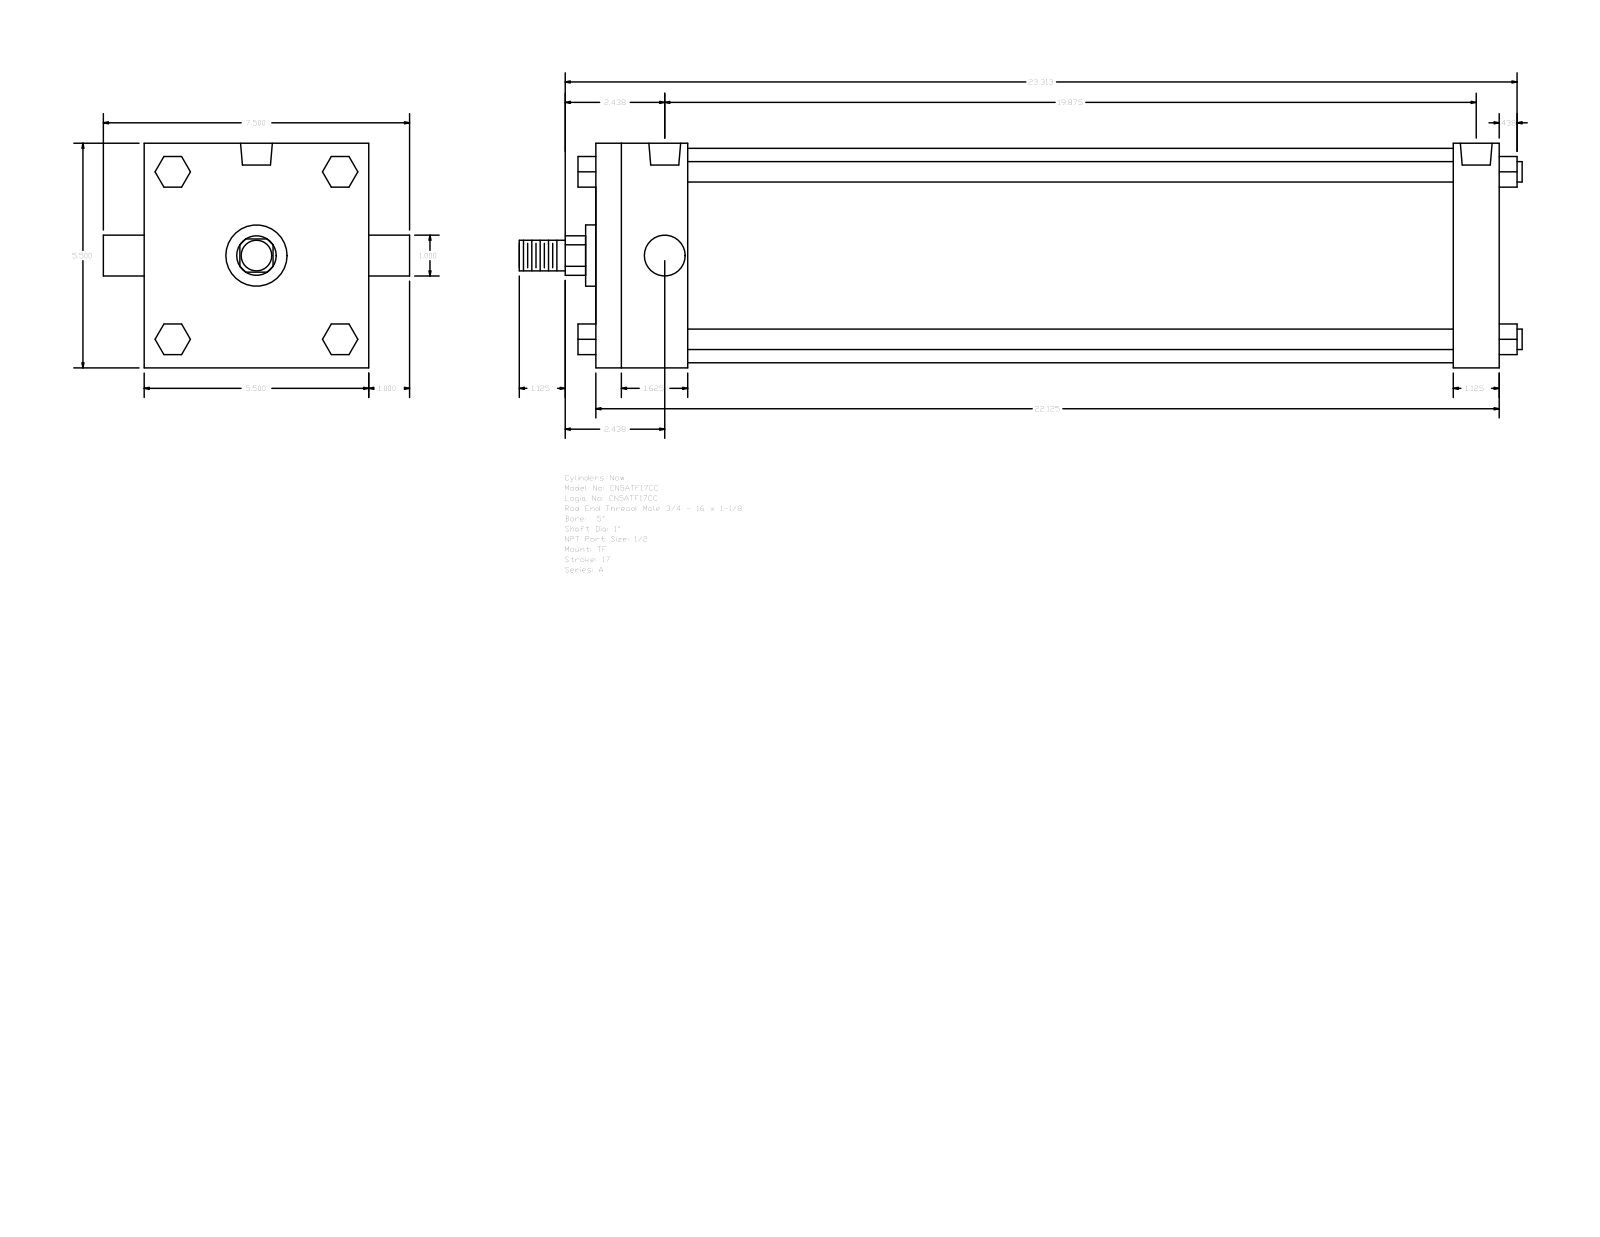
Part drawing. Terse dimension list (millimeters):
name: A_TF__0500_1
written by: GSSL Pune (CONFIG_CONTROL_DESIGN)
unit: mm
bodies: 0 solids, 120 faces (92 planar, 28 cylindrical, 0 other)
size: 623.89 × 190.5 × 139.7
holes: 3× ⌀8.73, 2× ⌀19.77
bosses: 4× ⌀12.7, 2× ⌀25.4, 1× ⌀133.35, 1× ⌀38.1, 1× ⌀19.05
rounds: 1× R12.29
face distances: 139.7, 561.97, 28.57, 533.4, 57.15, 476.25, 504.82, 19.05, 52.07, 90.18
hole spacings: 2.39, 502.44, 500.05, 504.83
